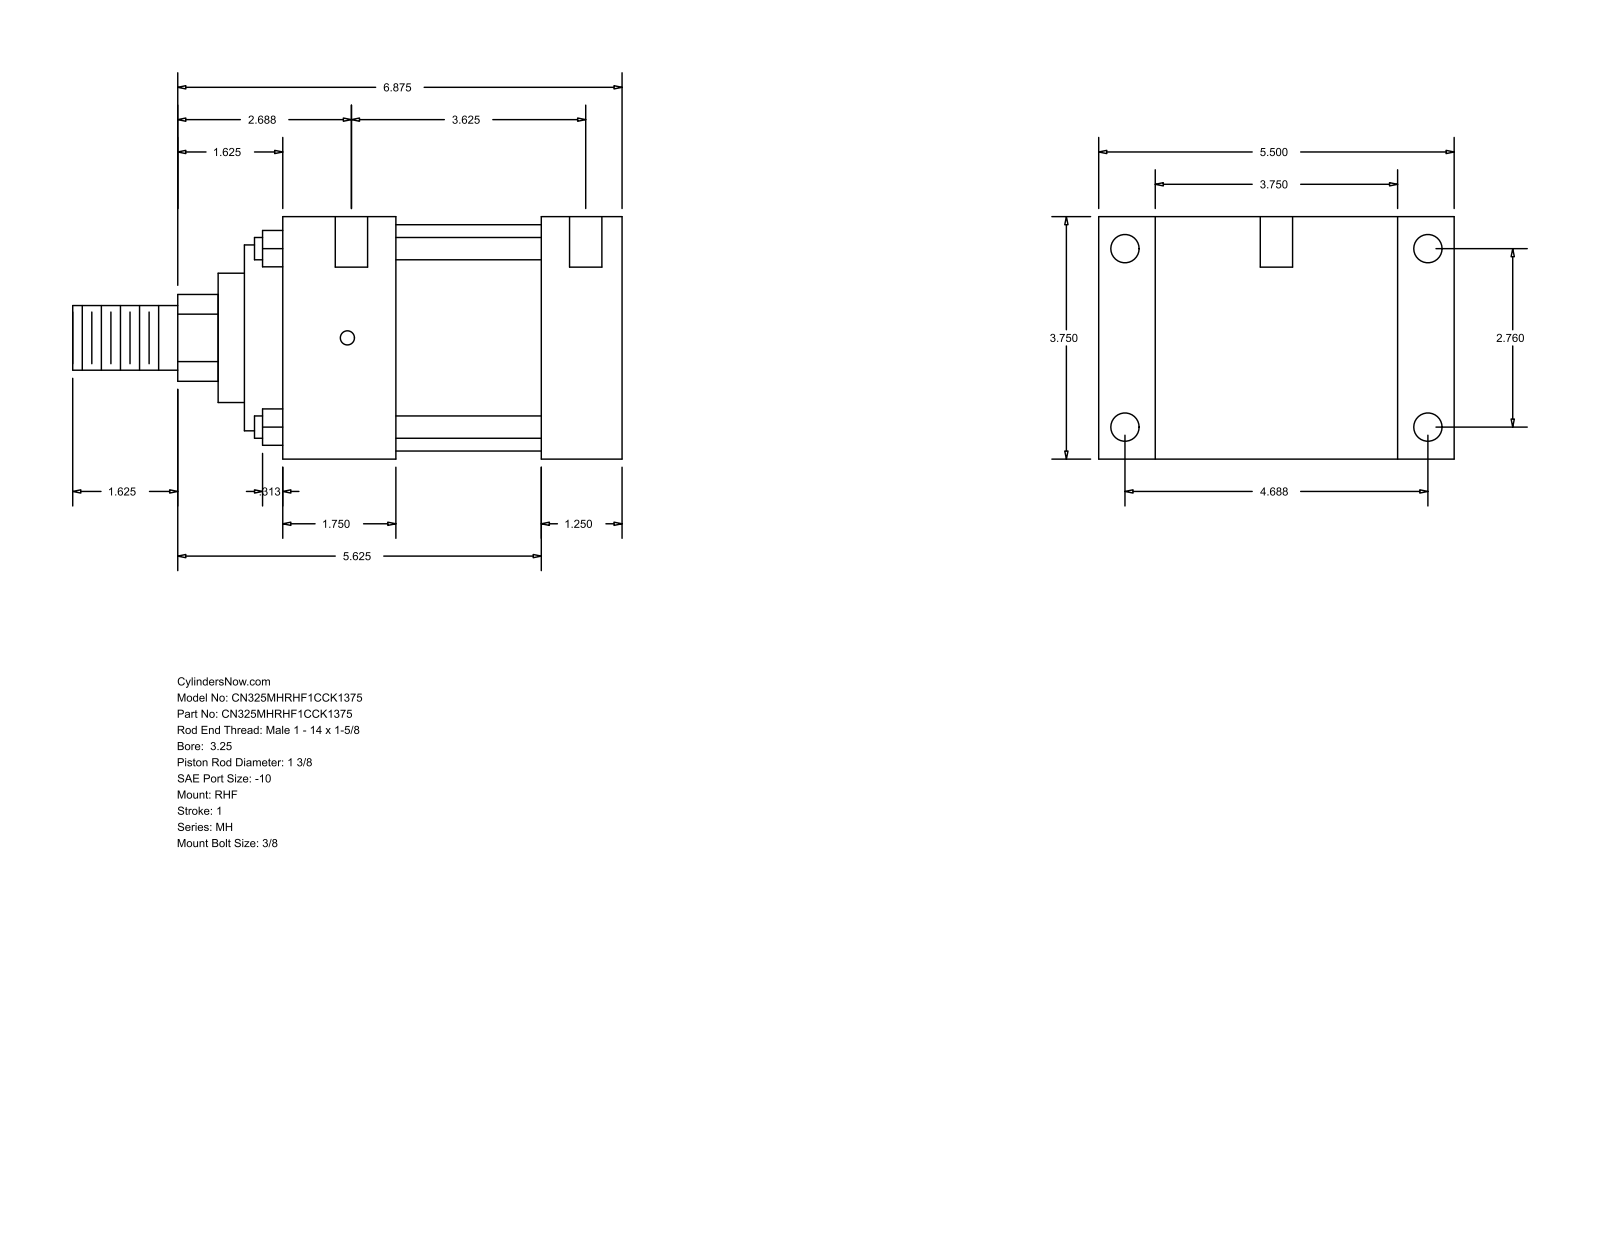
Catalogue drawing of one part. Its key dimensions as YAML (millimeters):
part_name: "MH_RHF__0325_1.375"
step_written_by: "GSSL Pune (CONFIG_CONTROL_DESIGN)"
units: millimeters
bodies: {solids: 0, faces: 90, planar: 61, cylindrical: 29, other: 0}
overall_size: [215.9, 139.7, 95.25]
round_holes:
  - {diameter: 5.56, count: 4}
  - {diameter: 11.13, count: 4}
  - {diameter: 12.7, count: 2}
round_bosses_or_shafts:
  - {diameter: 8.76, count: 4}
  - {diameter: 88.9, count: 1}
  - {diameter: 73.03, count: 1}
  - {diameter: 50.8, count: 1}
  - {diameter: 34.92, count: 1}
  - {diameter: 25.4, count: 1}
partial_cylinders:
  - {radius: 17.06, count: 1}
face_to_face_distances: [95.24, 31.74, 22.23, 117.47, 101.61, 133.35, 139.7, 44.45, 57.16, 88.9]
hole_center_spacings: [70.1, 98.43, 119.06, 138.16, 1.59, 4.76, 92.08, 93.67]
